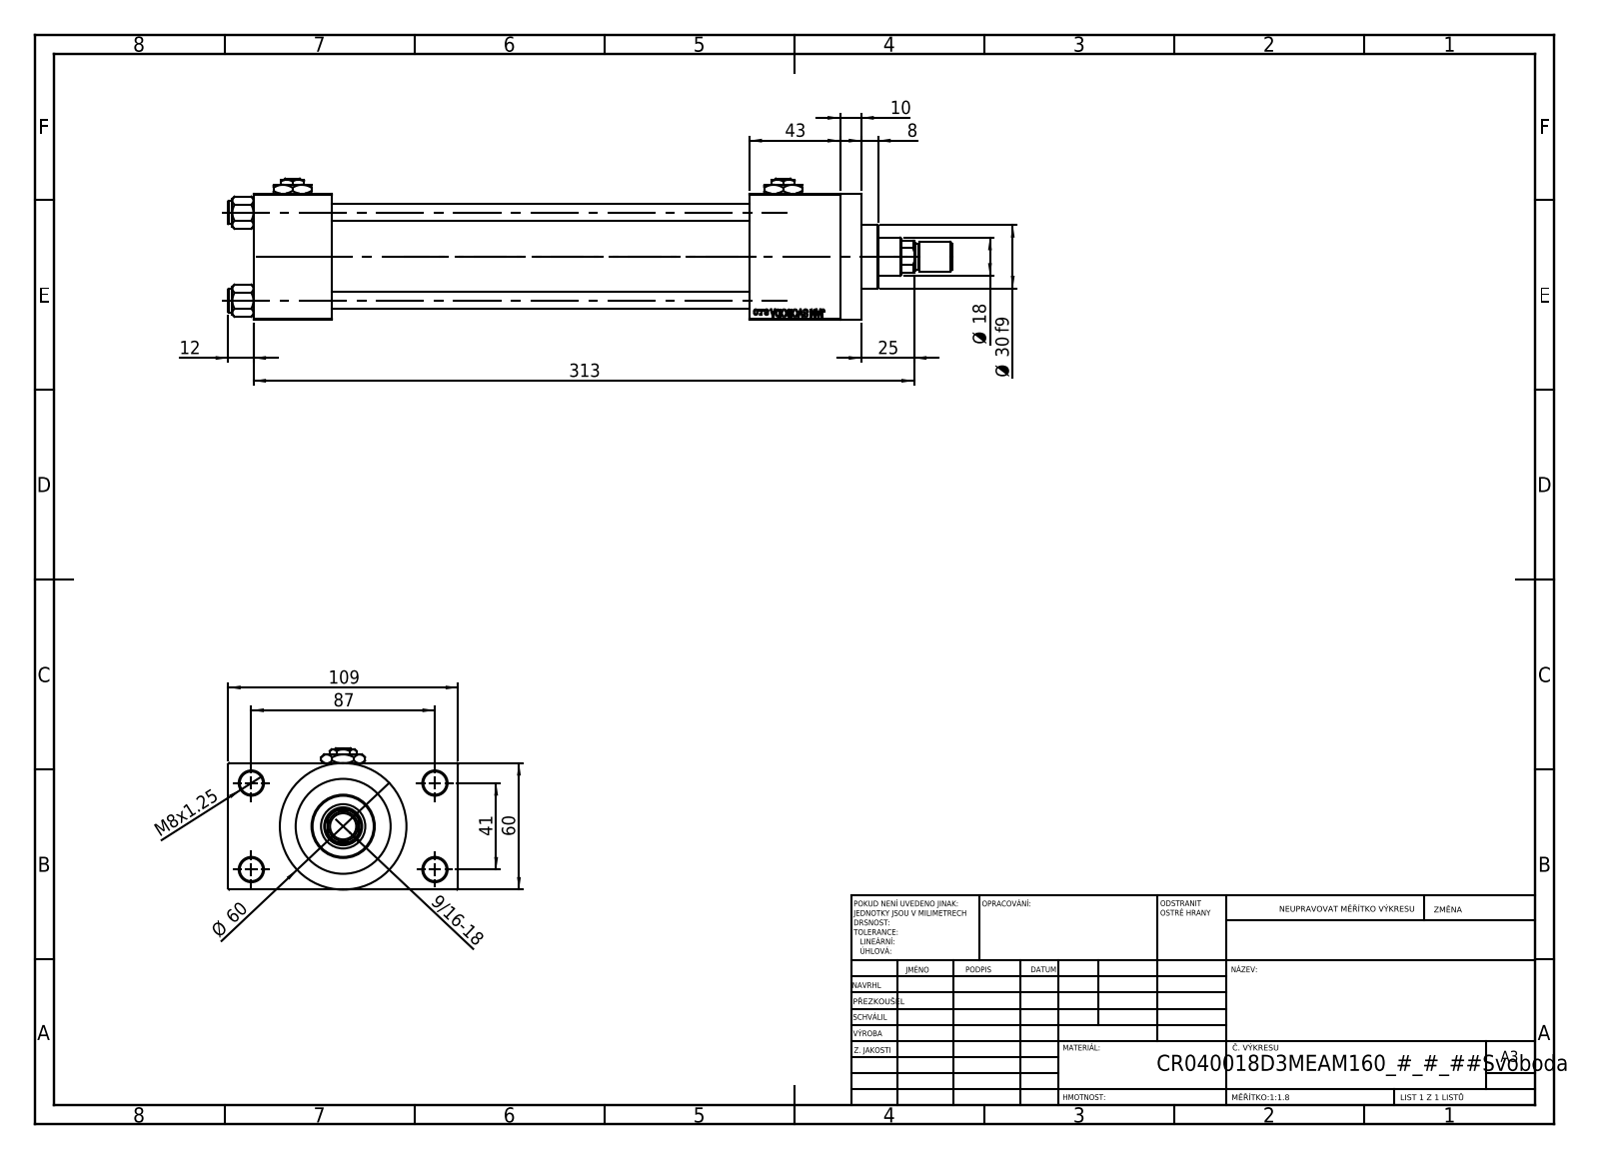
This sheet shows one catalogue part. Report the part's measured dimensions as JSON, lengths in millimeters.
{"part_name": "V215CR_D_Body; V215_VC_A; V215CR_VCP_D; NUT_M5_D (+3 more)", "step_written_by": "SolidWorks 2019 (CONFIG_CONTROL_DESIGN)", "units": "millimeters", "bodies": {"solids": 14, "faces": 1220, "planar": 550, "cylindrical": 104, "other": 566}, "overall_size": [343, 109, 67], "volume_mm3": 638776, "surface_area_mm2": 184857, "round_holes": [[8, 4], [11, 4], [7, 2], [16.66, 2], [24, 2], [8.5, 1], [18, 1], [21, 1], [31, 1], [40, 1], [45, 1]], "round_bosses_or_shafts": [[11, 4], [60, 1], [46, 1], [30, 1], [14, 1], [12, 1]], "partial_cylinders_radius": [[8.5, 1]], "face_to_face_distances": [60, 24.5, 84.5, 198, 37, 235, 43, 278, 241, 109], "hole_center_spacings": [22.65, 29.49, 41.7, 47.15, 48.09, 64.35, 76.49, 41]}
